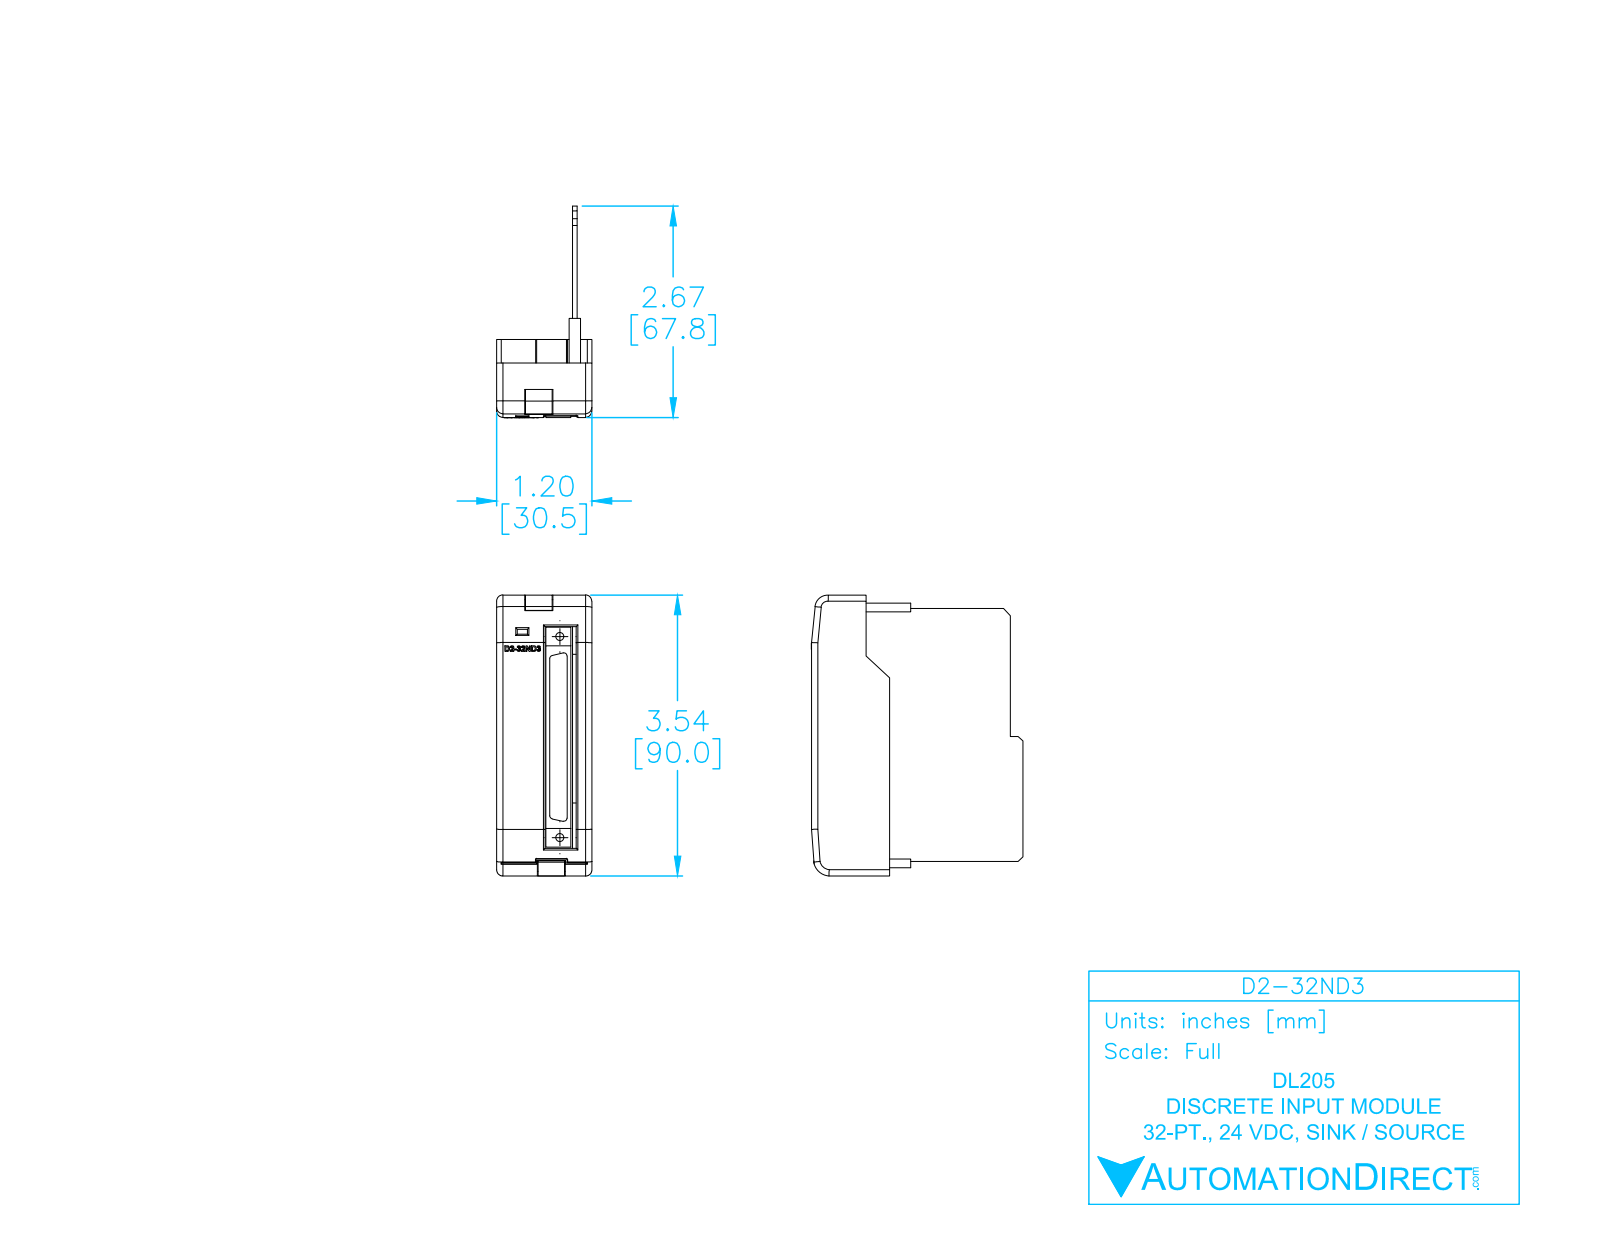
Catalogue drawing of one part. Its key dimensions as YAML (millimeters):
part_name: "D2-32ND3_ModuleCase_light_NEW"
step_written_by: "SolidWorks 2009 (AUTOMOTIVE_DESIGN)"
units: millimeters
bodies: {solids: 5, faces: 331, planar: 193, cylindrical: 63, other: 75}
overall_size: [90, 67.85, 30.5]
volume: 20870
surface_area: 29188
round_holes:
  - {diameter: 2.5, count: 2}
partial_cylinders:
  - {radius: 0.5, count: 24}
  - {radius: 2, count: 10}
  - {radius: 0.25, count: 4}
  - {radius: 1, count: 4}
  - {radius: 2.62, count: 1}
  - {radius: 3.79, count: 1}
  - {radius: 4.12, count: 1}
  - {radius: 5.29, count: 1}
face_to_face_distances: [1.5, 4.72, 3.22, 6.22, 24.28, 29, 0.5, 25.78, 30.5, 22.78]
hole_center_spacings: [64.38]
